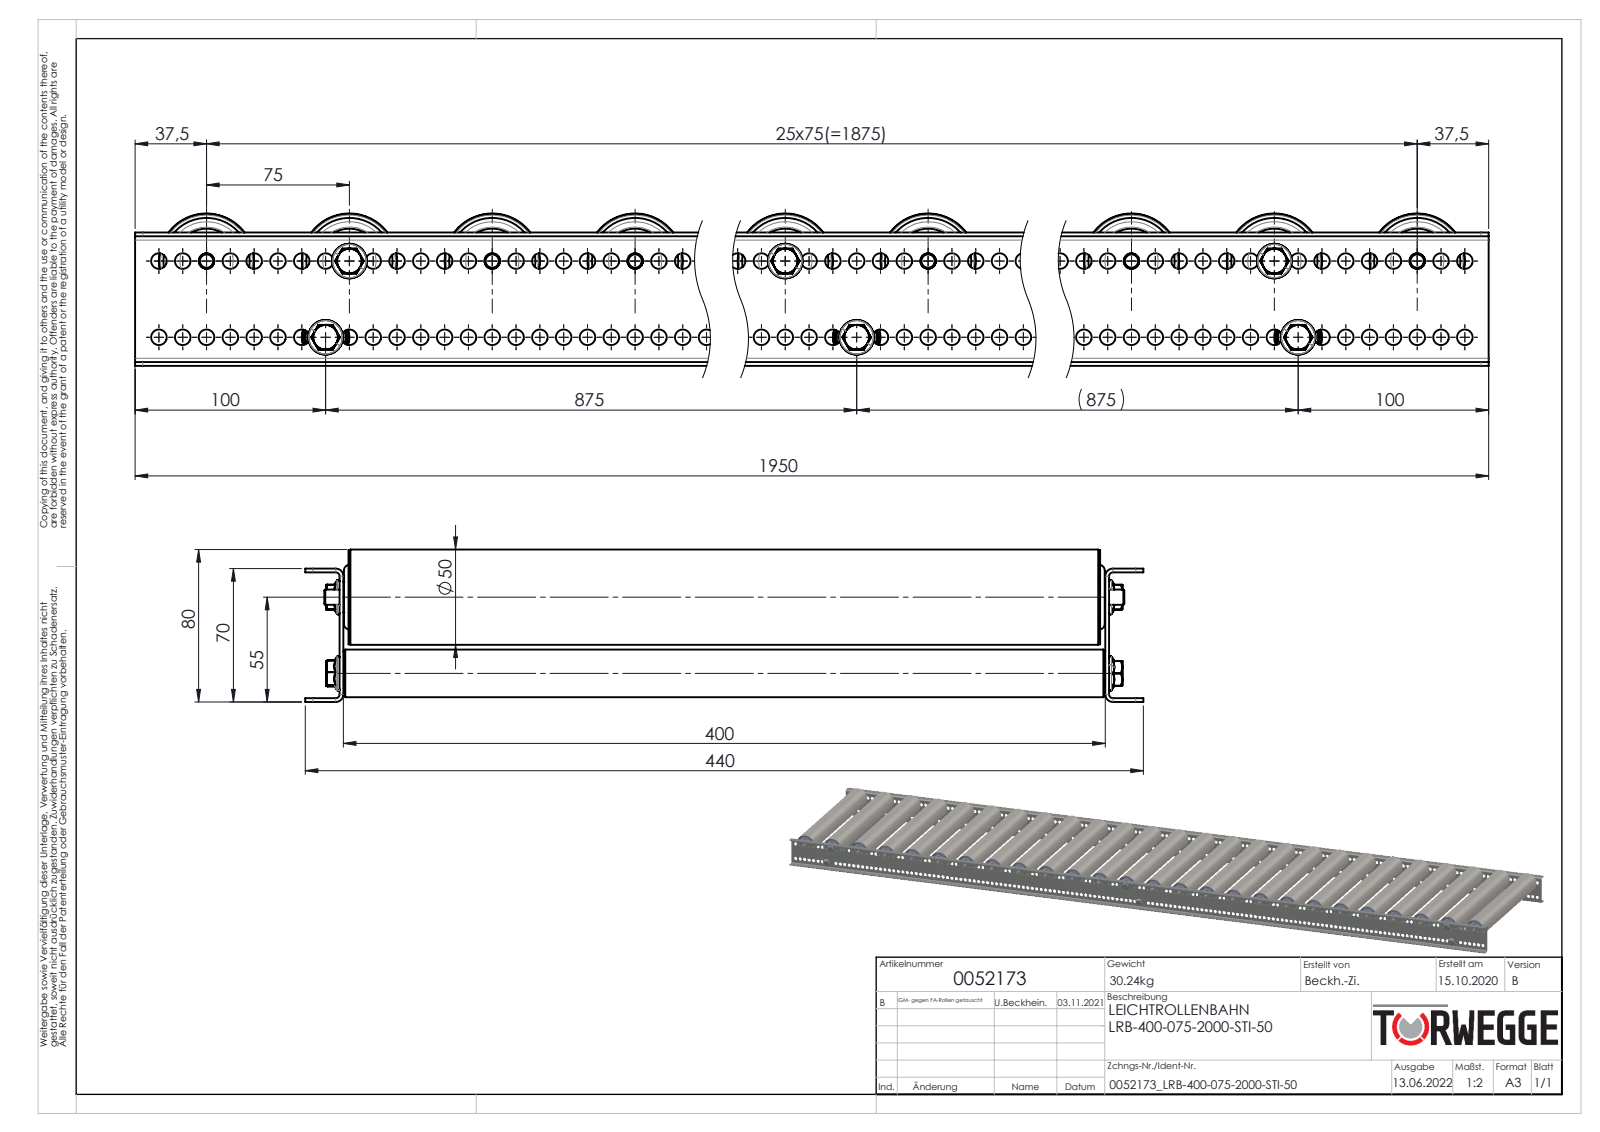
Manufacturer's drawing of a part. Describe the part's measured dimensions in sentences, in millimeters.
The part is named "Sicherungsring_DIN471_8x0.8_Circlip DIN 471 - 8 x 0.8; Tragrollenachse-Ø8_KFG_L=420; TRG-50x1,5-STI-A8-FA_KFG_0054465_TRG-50x1,5-STI-A8-FA-EL=400; 0039771_Tragrollenrohr-Ø50x1,5STI_KFG_EL400 (+8 more)". Its 3-D file was written by "SolidWorks 2020 (AUTOMOTIVE_DESIGN)". It is 602 solids with 10646 faces: 2112 planar, 3872 cylindrical and 4662 other. Overall it measures 1950 by 440 by 80 millimeters. Its volume is 4 370 000 cubic millimeters and its surface area 5 139 000 square millimeters. Round holes: 310 of diameter 8.2, 26 of diameter 17.1, 26 of diameter 18.5, 26 of diameter 27.7, 26 of diameter 45.3, 26 of diameter 47, 23 of diameter 7.6, 6 of diameter 6.8, 3 of diameter 12, 3 of diameter 12.2, 3 of diameter 19.2, 3 of diameter 21. Round bosses or shafts: 29 of diameter 8, 26 of diameter 50, 26 of diameter 49.5, 26 of diameter 47.3, 26 of diameter 29.7, 26 of diameter 27.4, 26 of diameter 27.3, 26 of diameter 16. Partial cylindrical surfaces (rounded edges, fillets, slot ends): 46 of radius 0.6, 46 of radius 0.75, 46 of radius 2.45, 23 of radius 4.87, 23 of radius 7, 12 of radius 2.5, 8 of radius 4, 4 of radius 2. The main face-to-face distances are 2, 402, 68, 400, 404, 70, 66, 1, 2.3, 401.7. The hole center spacings are 12.5, 25, 37.5, 50, 62.5, 75, 87.5, 100.
